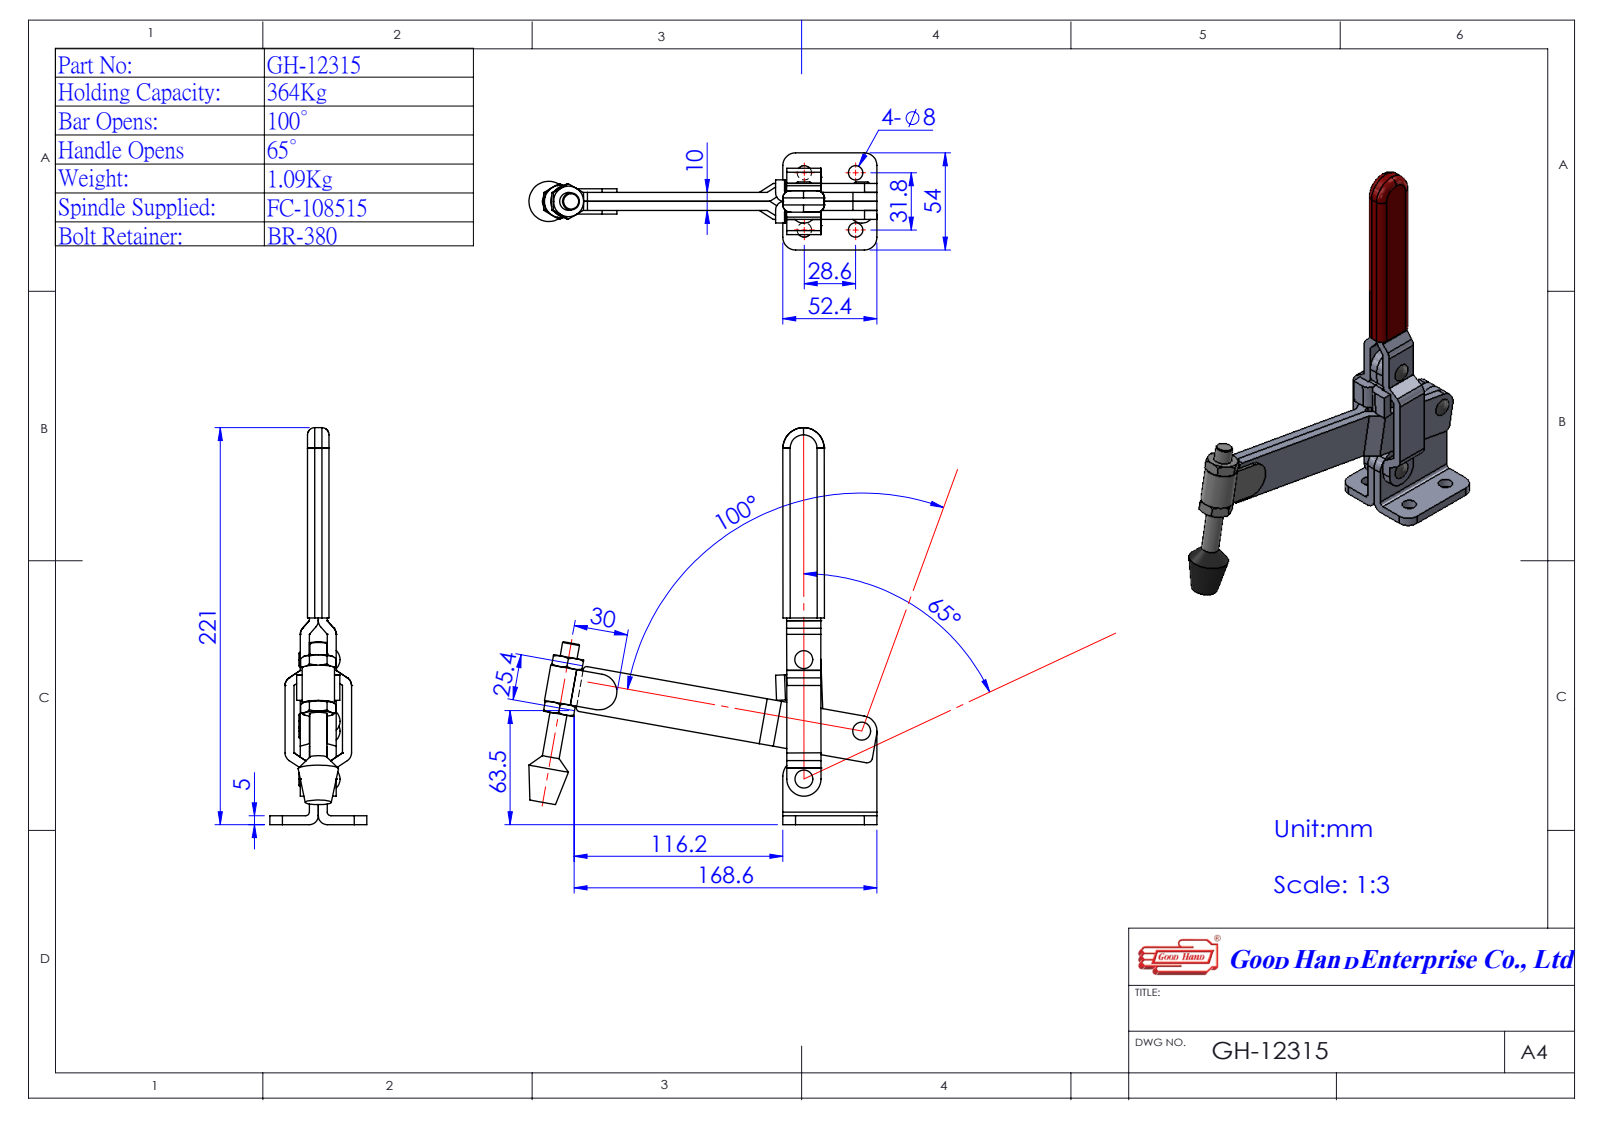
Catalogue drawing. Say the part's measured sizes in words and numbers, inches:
The part is named "Group1^GH-12315(簡化); Group2^GH-12315(簡化); Group5^GH-12315(簡化); Group4^GH-12305(簡化) (+2 more)". Its 3-D file was written by "SolidWorks 2016 (AUTOMOTIVE_DESIGN)". It is 5 solids with 296 faces: 133 planar, 115 cylindrical and 48 other. Overall it measures 8.701 by 7.979 by 2.126 inches. Its volume is 9.373 cubic inches and its surface area 98.61 square inches. Round holes: 4 of diameter 0.157, 4 of diameter 0.315, 1 of diameter 0.248. Round bosses or shafts: 1 of diameter 0.375, 1 of diameter 0.248. Partial cylindrical surfaces (rounded edges, fillets, slot ends): 10 of radius 0.004, 8 of radius 0.157, 6 of radius 0.079, 5 of radius 0.276, 4 of radius 0.039, 4 of radius 0.201, 4 of radius 0.201, 3 of radius 0.374. The main face-to-face distances are 0.197, 0.394, 0.039, 0.591, 0.335, 0.531, 0.236, 0.157, 0.728, 0.925. The hole center spacings are 1.126, 1.252, 1.684, 1.236, 1.27, 1.351, 1.647, 2.017.
